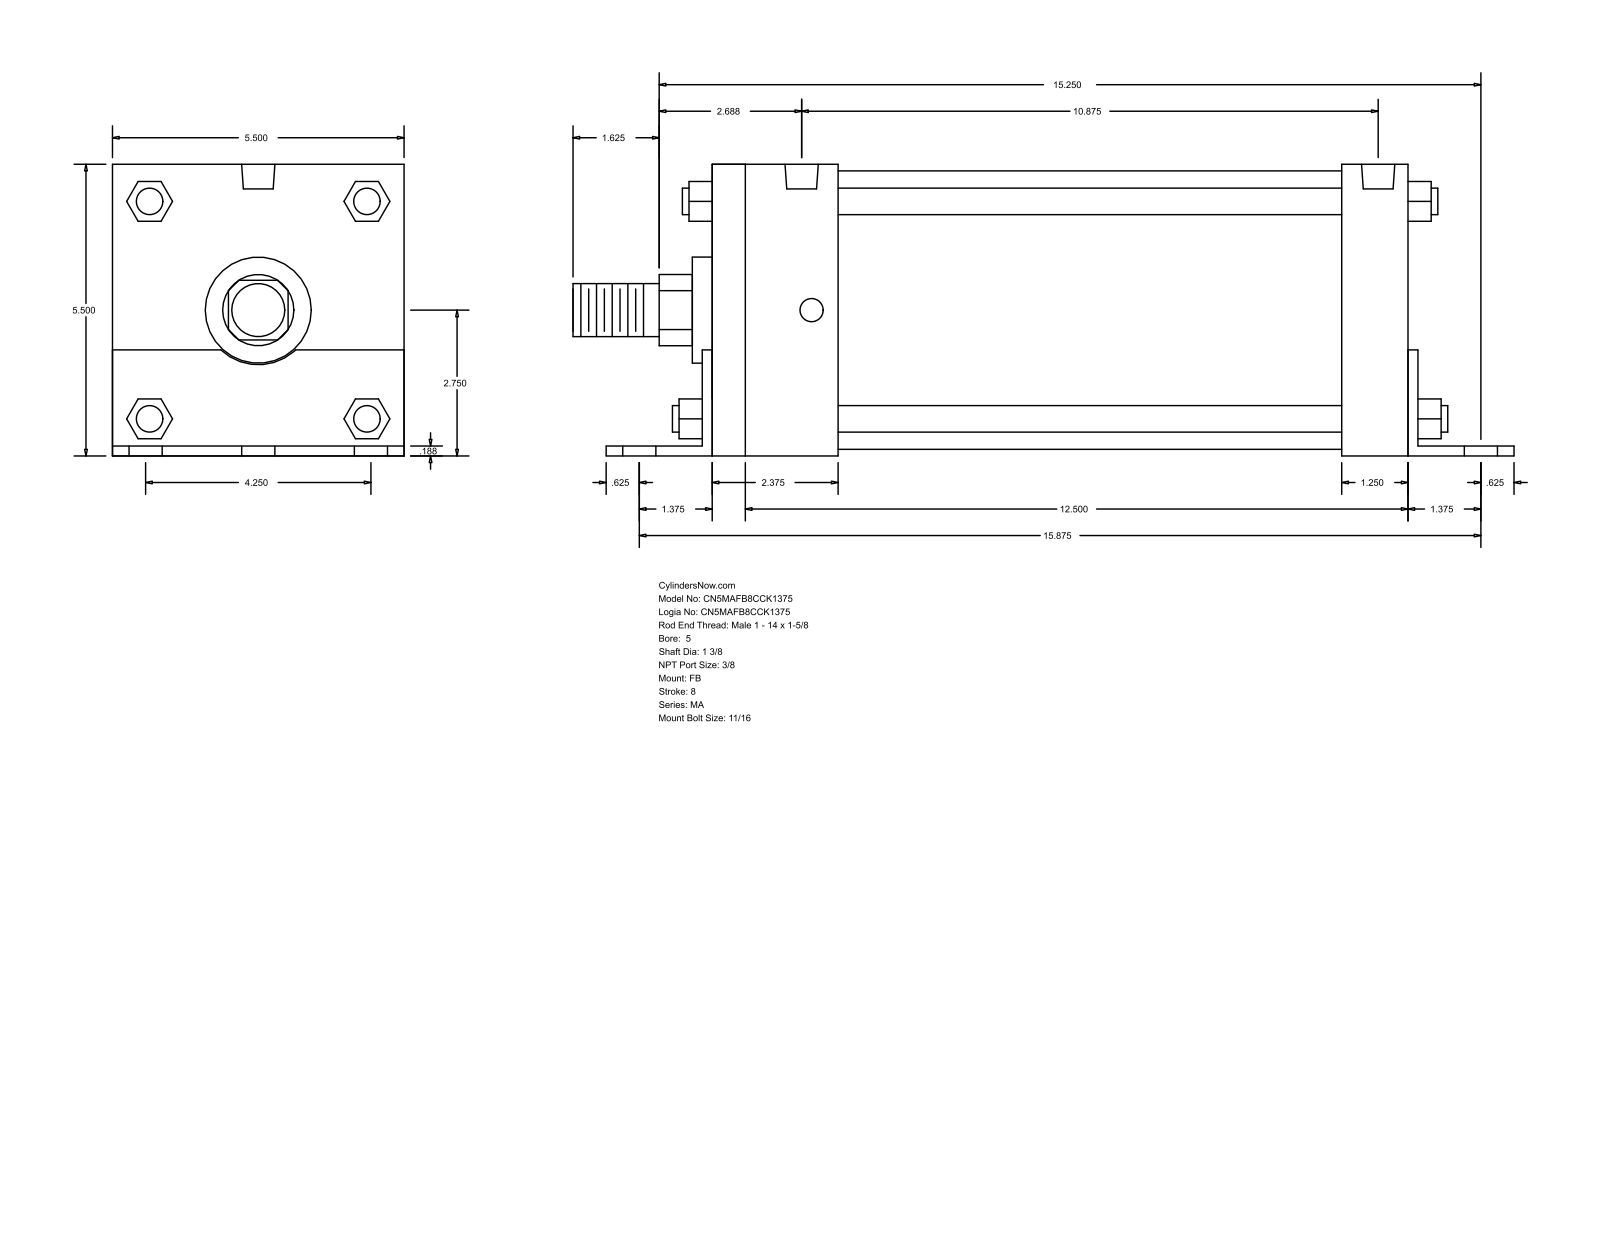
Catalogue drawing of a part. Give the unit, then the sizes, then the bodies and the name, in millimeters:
Units: millimetres
Overall size (bounding box): 450.85 × 139.75 × 139.7
Round holes (diameter × count): ⌀17.46 ×6, ⌀11.11 ×4, ⌀15.93 ×2
Round bosses / shafts (diameter × count): ⌀12.7 ×4, ⌀133.35 ×1, ⌀50.8 ×1, ⌀34.92 ×1, ⌀25.4 ×1
Partial cylindrical surfaces — rounded edges, fillets, slot ends (radius × count): R17.06 ×1, R26.16 ×1
Main face-to-face distances: 139.7, 4.76, 139.75, 4.71, 134.99, 333.37, 4.77, 338.14, 338.13, 342.9
Hole centre spacings: 53.98, 406.83, 403.23, 73.04, 76.33, 94.68, 98.64, 107.96
Bodies: 0 solids, 140 faces (105 planar, 35 cylindrical, 0 other)
Part name (STEP PRODUCT): MA_FB__0500_1.375
STEP written by: GSSL Pune (CONFIG_CONTROL_DESIGN)
